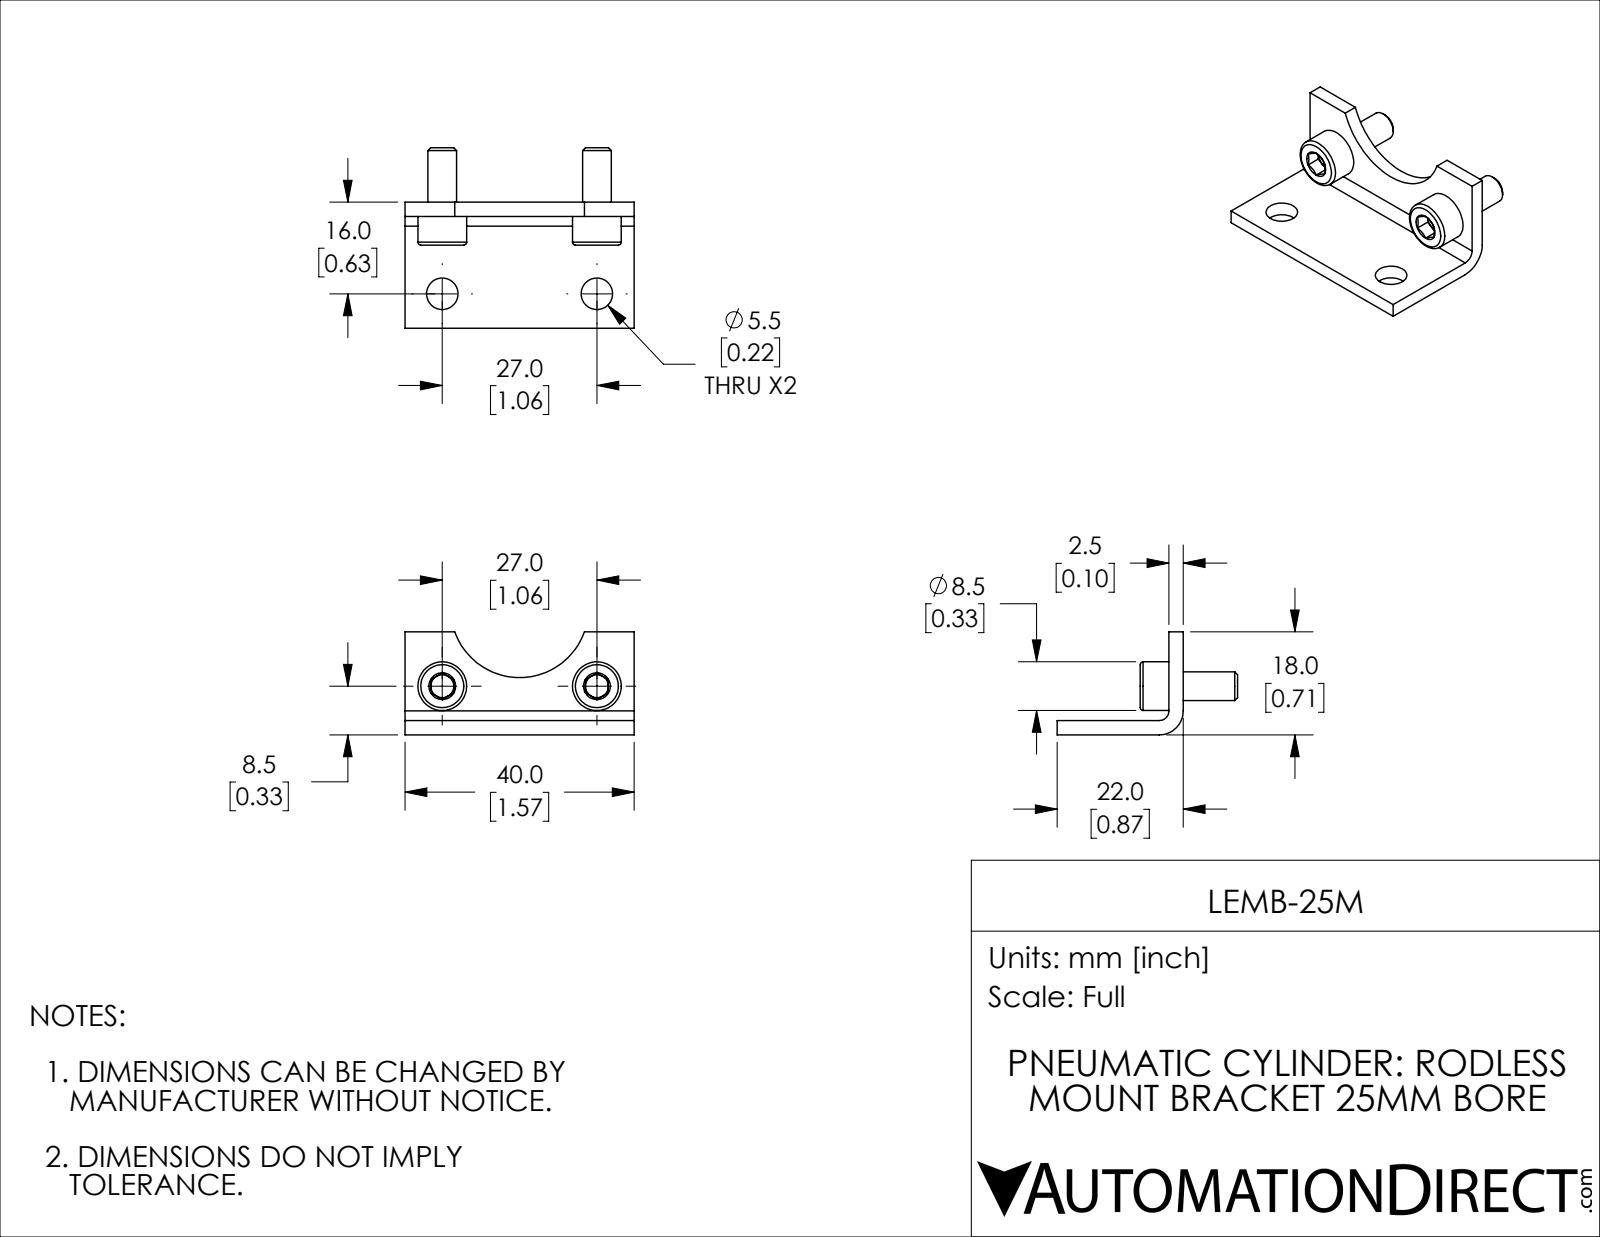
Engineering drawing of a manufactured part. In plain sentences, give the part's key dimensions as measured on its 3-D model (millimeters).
The part is named "LEMB-25M". Its 3-D file was written by "SolidWorks 2019 (CONFIG_CONTROL_DESIGN)". It is 3 solids with 86 faces: 39 planar, 19 cylindrical and 28 other. Overall it measures 40 by 31.5 by 18 millimeters. Its volume is 4 030 cubic millimeters and its surface area 3 939 square millimeters. Round holes: 2 of diameter 5, 2 of diameter 5.5. Round bosses or shafts: 2 of diameter 8.5. Partial cylindrical surfaces (rounded edges, fillets, slot ends): 1 of radius 1.7, 1 of radius 4.2, 1 of radius 12. The main face-to-face distances are 2.5, 22, 19.5, 40, 14.5, 5, 7.5, 18, 15.5, 31.5. The hole center spacings are 27.
